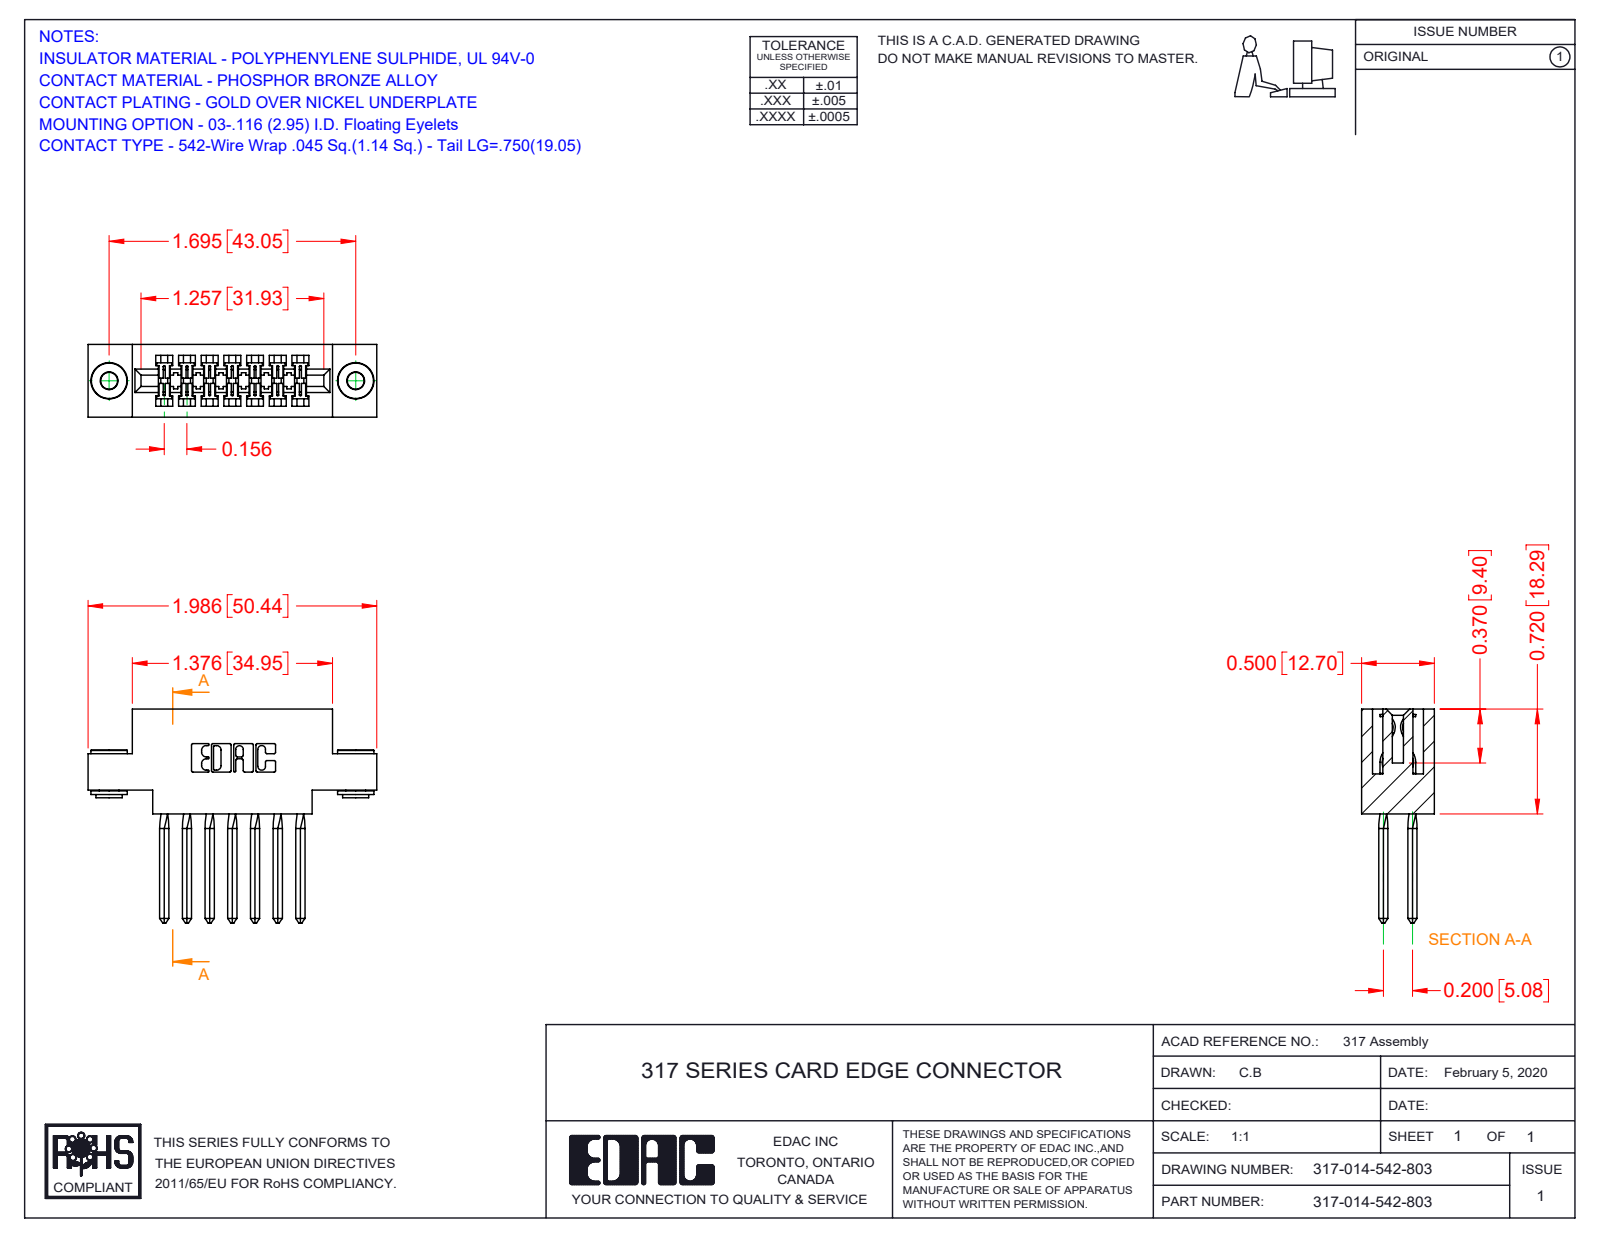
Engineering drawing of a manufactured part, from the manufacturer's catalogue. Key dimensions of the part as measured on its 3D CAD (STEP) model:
Part name (STEP PRODUCT): 345-250-002_345-250-002-102; 317-014-542-803; 317 Part_.156 Dia - TH; 317-290-003_542
STEP written by: SolidWorks 2016 (CONFIG_CONTROL_DESIGN)
Units: inches
Bodies: 17 solids, 938 faces (712 planar, 162 cylindrical, 64 other)
Overall size (bounding box): 1.986 × 1.47 × 0.5
Volume: 0.438 in³ · Surface area: 14.06 in²
Round holes (diameter × count): ⌀0.116 ×2, ⌀0.156 ×2
Round bosses / shafts (diameter × count): ⌀0.25 ×2, ⌀0.18 ×2, ⌀0.136 ×2
Partial cylindrical surfaces — rounded edges, fillets, slot ends (radius × count): R0.006 ×28, R0.01 ×22, R0.007 ×6, R0.031 ×6, R0.026 ×3, R0.074 ×2, R0.089 ×2, R0.1 ×2
Main face-to-face distances: 0.5, 0.11, 0.075, 0.425, 0.156, 0.116, 0.22, 0.065, 0.163, 0.136
Hole centre spacings: 1.695
